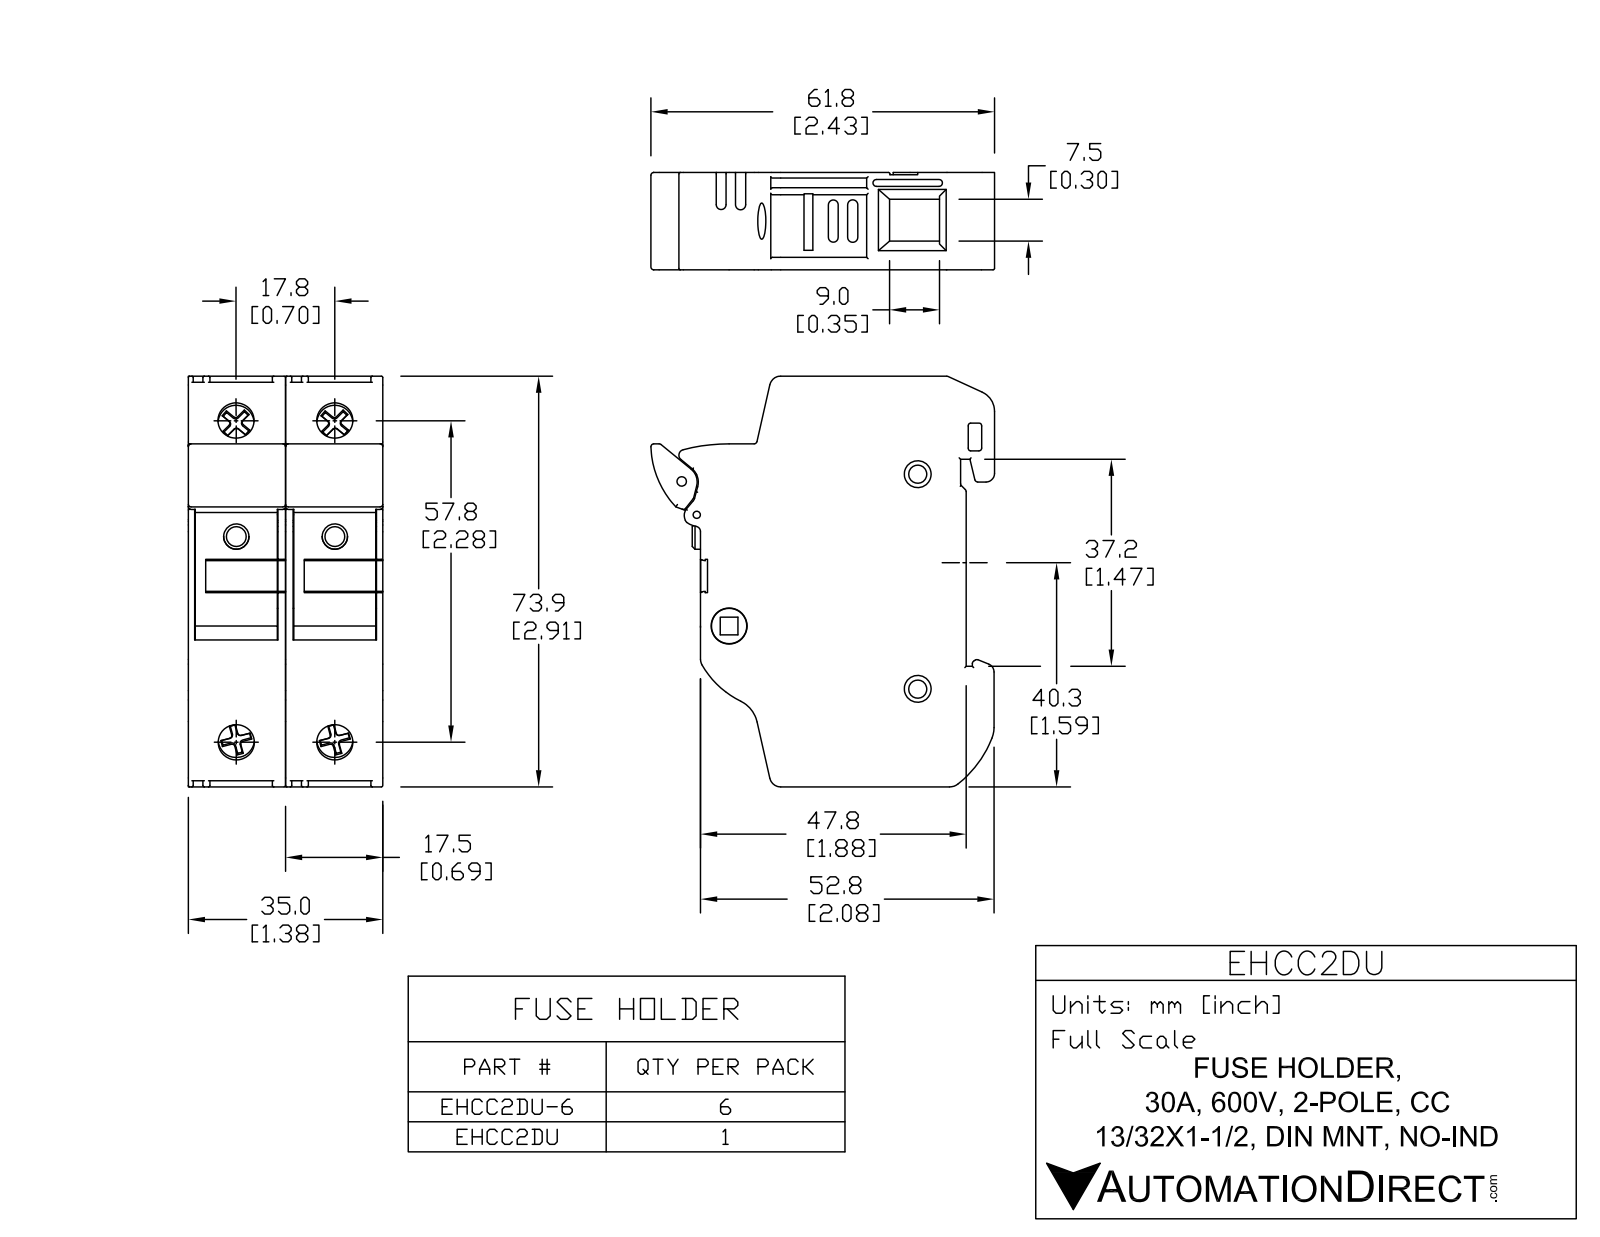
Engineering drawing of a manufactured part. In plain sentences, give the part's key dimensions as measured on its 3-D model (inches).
The part is named "EHCC2DU". Its 3-D file was written by "SolidWorks 2017 (AUTOMOTIVE_DESIGN)". It is 1 solid with 1062 faces: 497 planar, 333 cylindrical and 232 other. Overall it measures 2.909 by 2.434 by 1.378 inches. Its volume is 6.437 cubic inches and its surface area 52.66 square inches. Round holes: 4 of diameter 0.256, 2 of diameter 0.128, 2 of diameter 0.19, 1 of diameter 0.051, 1 of diameter 0.067, 1 of diameter 0.255. Round bosses or shafts: 2 of diameter 0.179, 1 of diameter 0.25. Partial cylindrical surfaces (rounded edges, fillets, slot ends): 99 of radius 0.01, 11 of radius 0.02, 10 of radius 0.079, 9 of radius 0.02, 8 of radius 0.025, 7 of radius 0.039, 6 of radius 0.035, 6 of radius 0.036. The main face-to-face distances are 0.689, 1.378, 0.049, 0.062, 0.64, 1.083, 1.145, 0.903, 0.973, 0.016. The hole center spacings are 0.689, 0.259, 0.82, 1.077, 1.408, 1.409, 1.52, 1.522.
